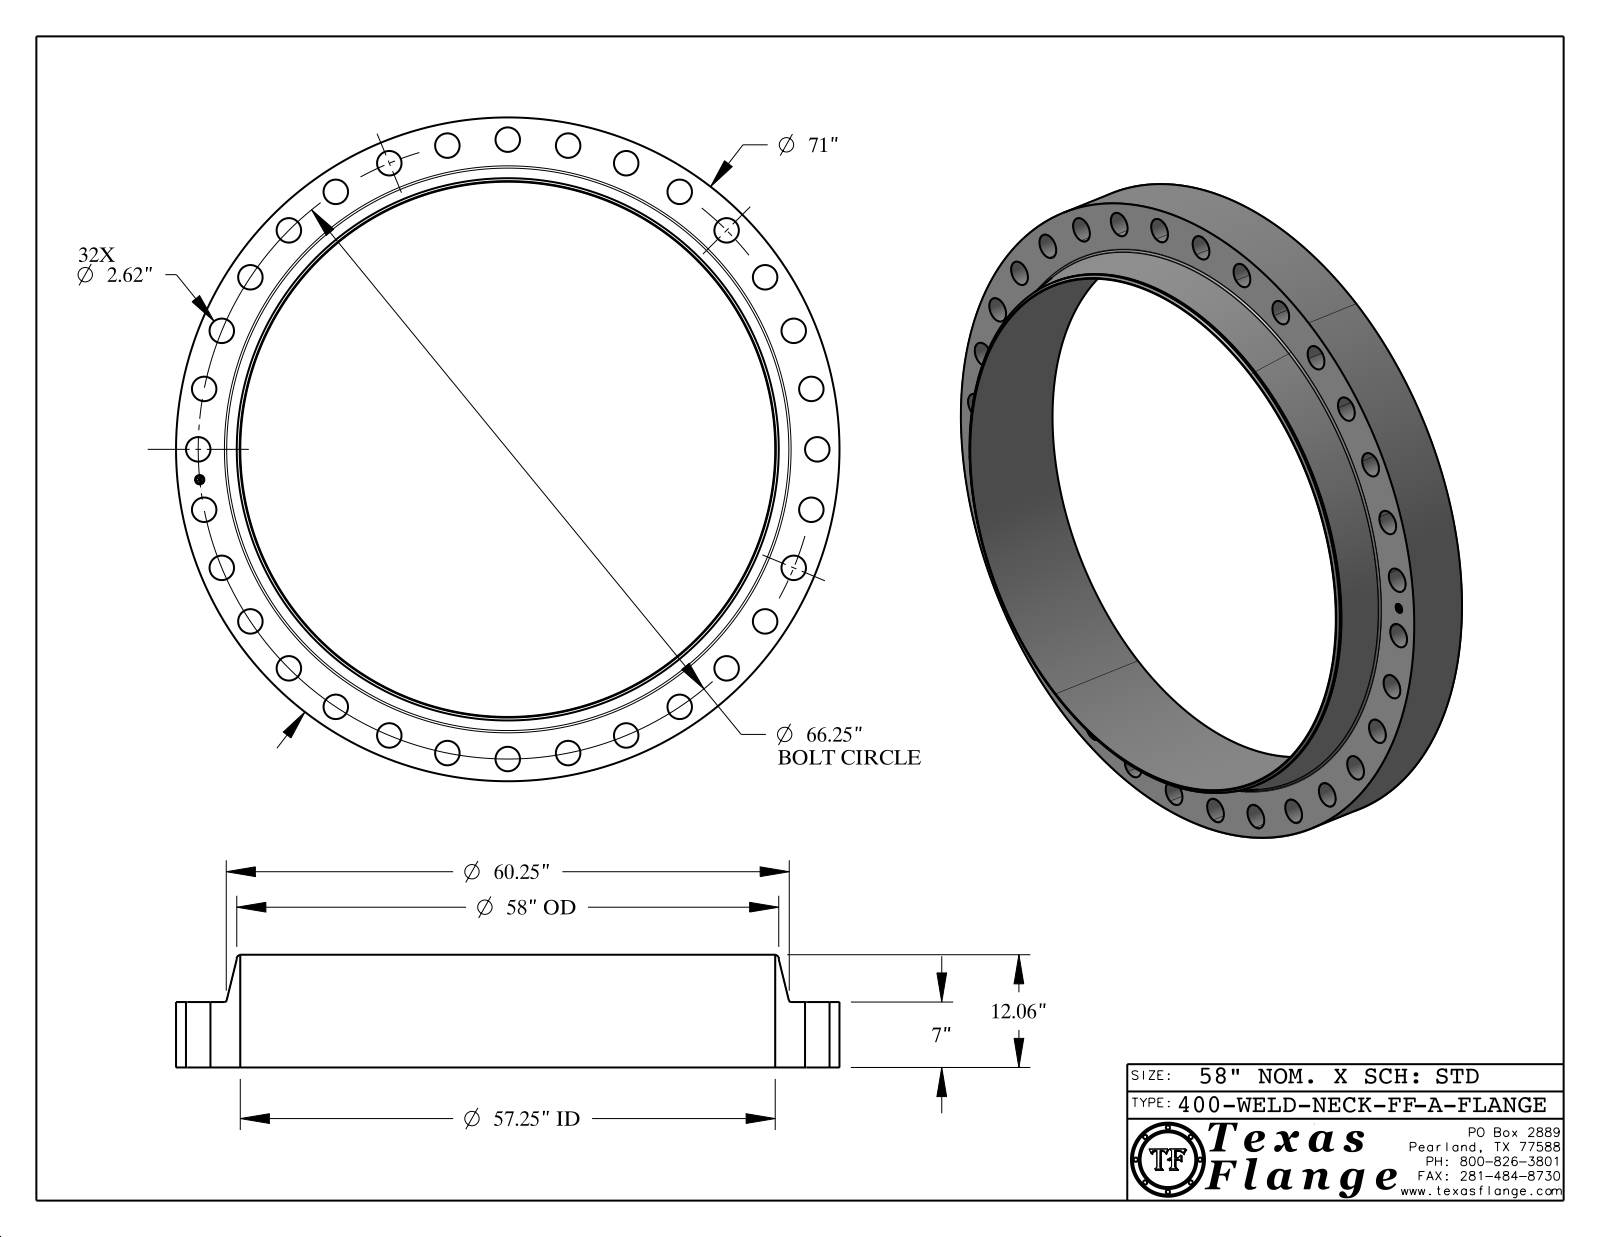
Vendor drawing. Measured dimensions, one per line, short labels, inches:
name: 400-WELD-NECK-FF, Series A
written by: CATIA V5 STEP AP214 (AUTOMOTIVE_DESIGN)
unit: in
bodies: 1 solid, 464 faces (368 planar, 90 cylindrical, 6 other)
size: 71 × 71 × 12.06
volume: 9 301 in³; area: 8 714 in²
holes: 32× ⌀2.62, 1× ⌀1, 1× ⌀57.25
bosses: 8× ⌀0.061, 1× ⌀71, 1× ⌀58, 1× ⌀0.788
face distances: 7, 12.06, 5.06, 0.015, 6.985, 5.075, 0.298, 0.292, 0.054, 0.193
hole spacings: 61.207, 33.125, 6.494, 12.925, 46.846, 63.397, 65.931, 64.977
